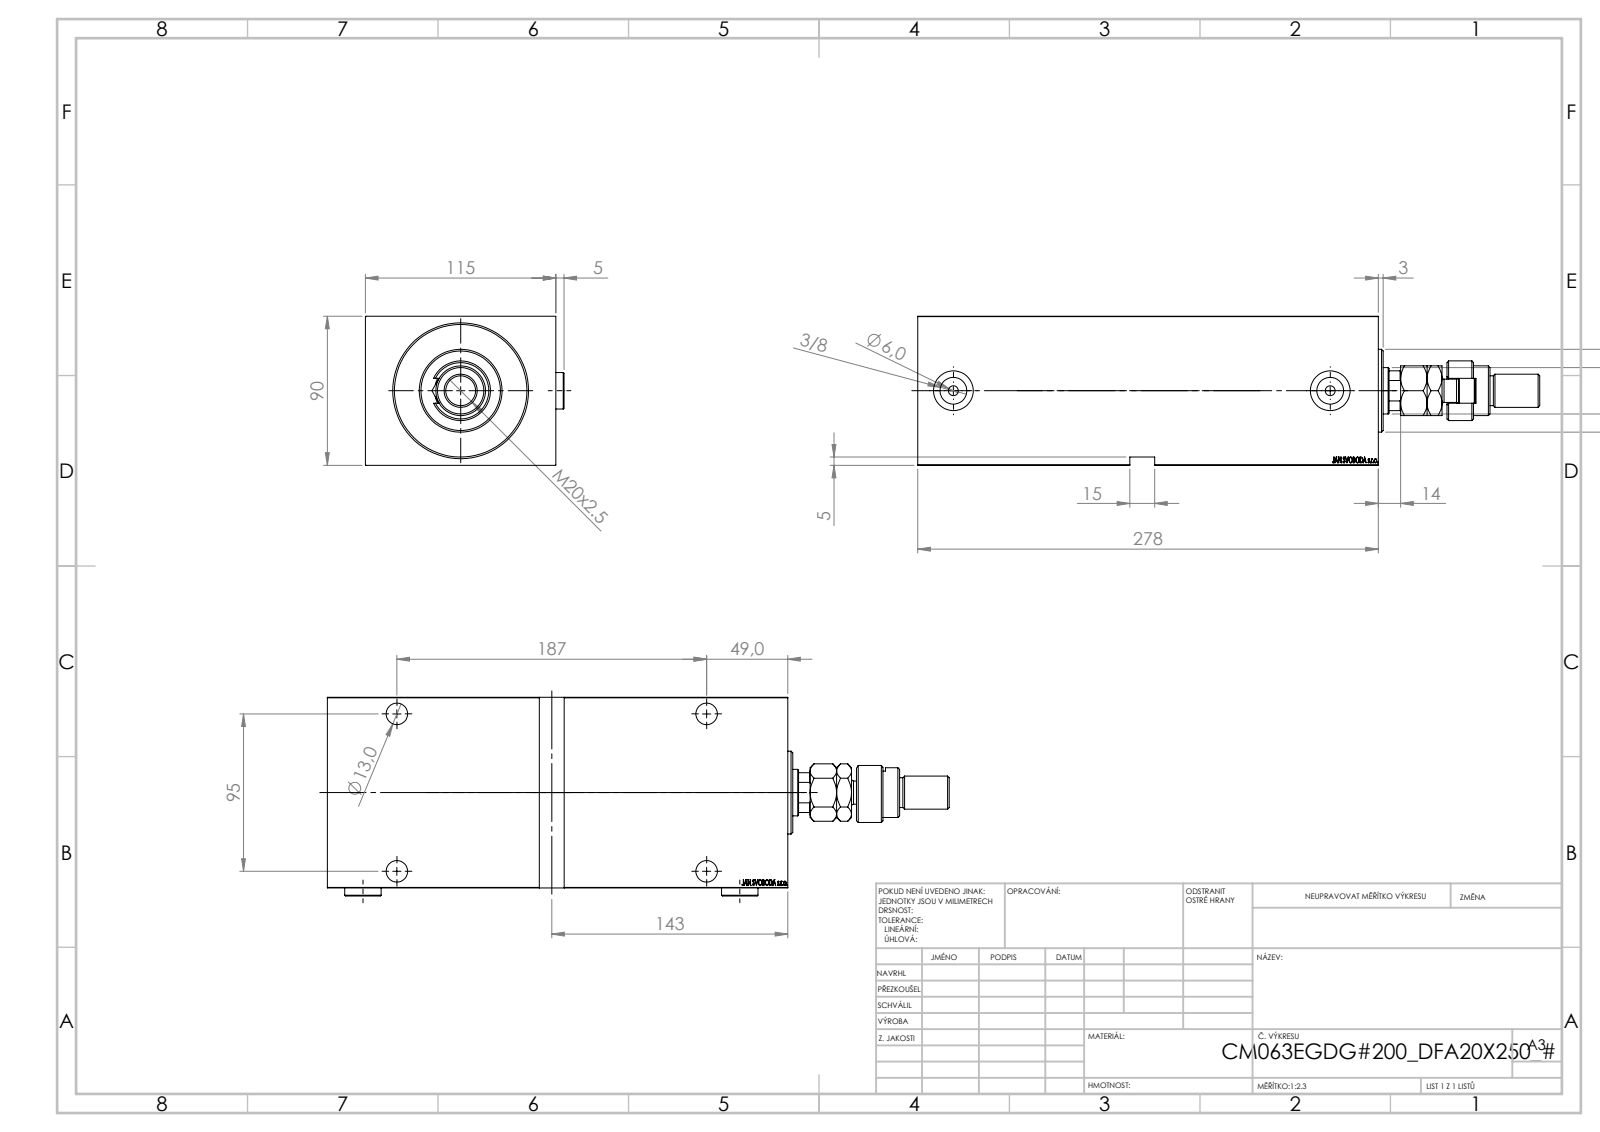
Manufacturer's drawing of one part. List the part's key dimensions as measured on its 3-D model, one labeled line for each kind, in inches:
Part name (STEP PRODUCT): Zatka_OIL_PORT; FEMALE_PART_FOR_DFA; V450CM_E_VCP; V450CM_VC_B (+2 more)
STEP written by: SolidWorks 2019 (CONFIG_CONTROL_DESIGN)
Units: inches
Bodies: 7 solids, 997 faces (474 planar, 81 cylindrical, 442 other)
Overall size (bounding box): 14.783 × 4.72 × 3.543
Volume: 144.1 in³ · Surface area: 423.4 in²
Round holes (diameter × count): ⌀0.512 ×4, ⌀0.748 ×4, ⌀0.236 ×2, ⌀0.637 ×2, ⌀0.945 ×2, ⌀0.728 ×1, ⌀1.102 ×1, ⌀1.24 ×1, ⌀2.48 ×1, ⌀3.15 ×1
Round bosses / shafts (diameter × count): ⌀0.866 ×3, ⌀2.559 ×1, ⌀1.969 ×1, ⌀1.417 ×1, ⌀1.181 ×1, ⌀0.787 ×1, ⌀0.709 ×1, ⌀0.551 ×1
Partial cylindrical surfaces — rounded edges, fillets, slot ends (radius × count): R0.295 ×1, R0.472 ×1, R0.531 ×1
Main face-to-face distances: 3.543, 4.528, 10.945, 0.689, 10.256, 0.197, 10.748, 10.059, 2.539, 8.209
Hole centre spacings: 3.74, 7.362, 8.258, 8.957
